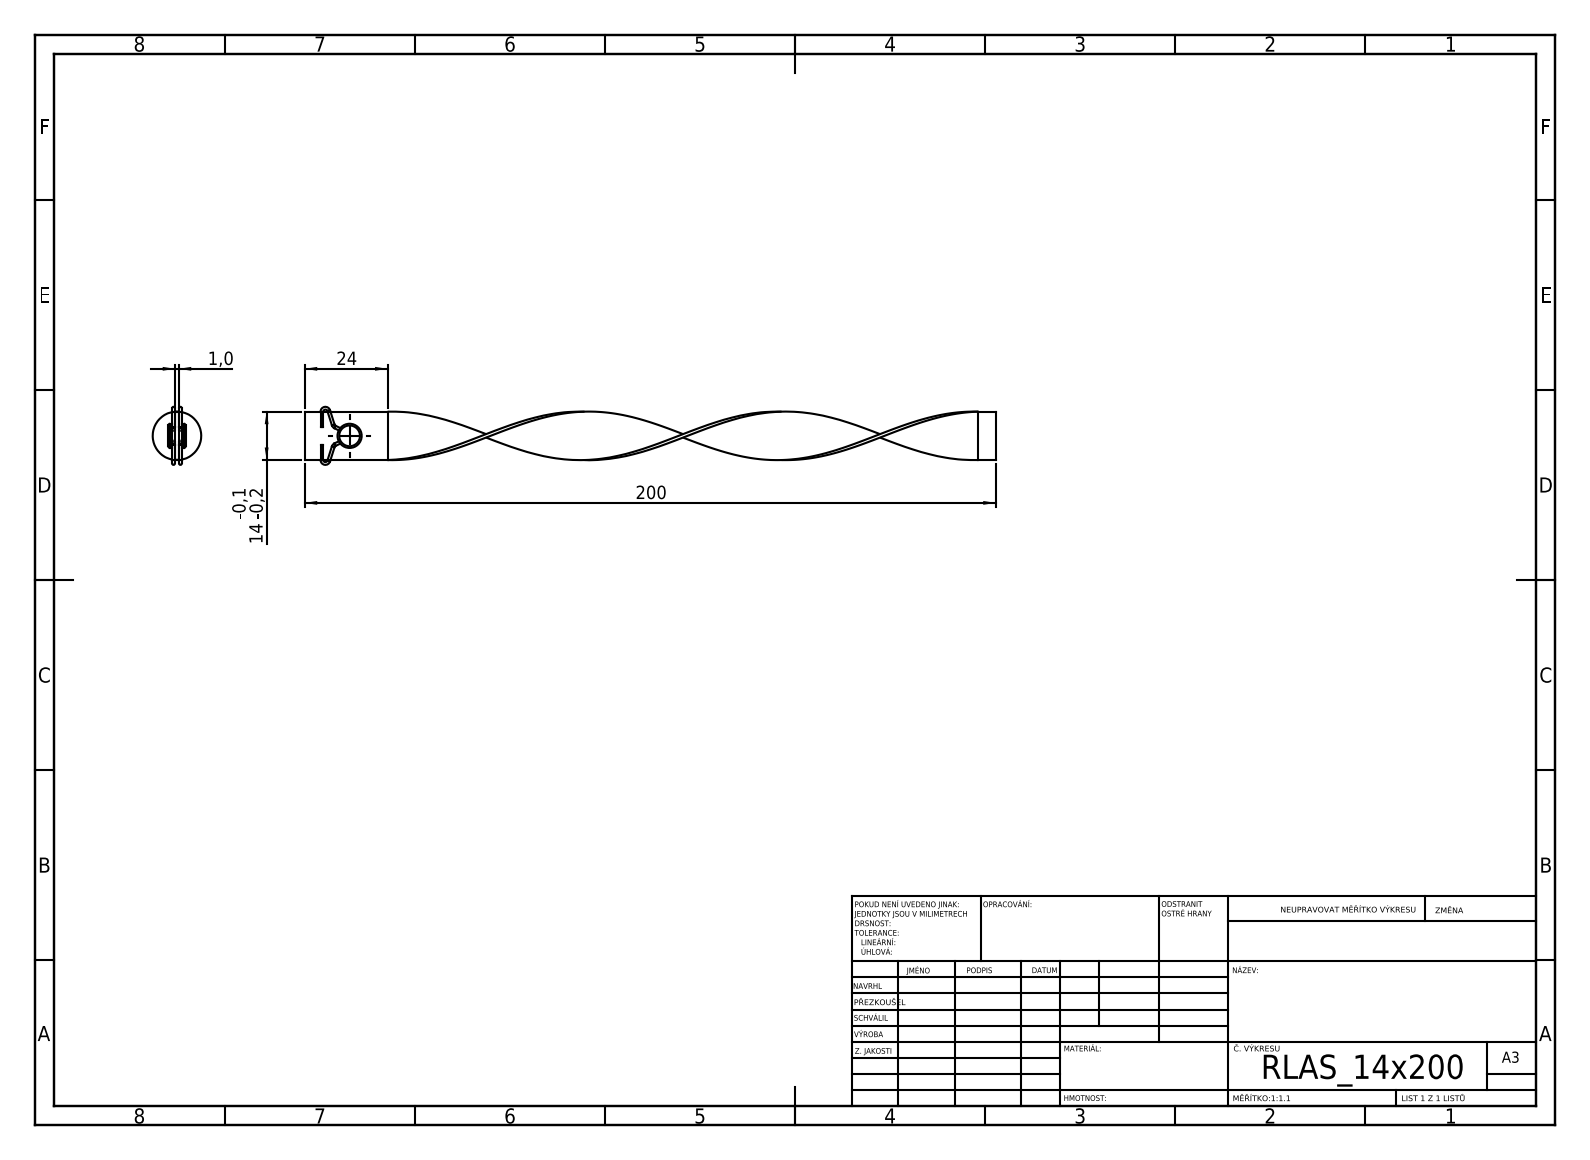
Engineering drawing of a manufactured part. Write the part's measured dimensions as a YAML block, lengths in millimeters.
step_written_by: "SolidWorks 2019 (CONFIG_CONTROL_DESIGN)"
units: millimeters
bodies: {solids: 3, faces: 90, planar: 18, cylindrical: 40, other: 32}
overall_size: [200, 16.8, 14.04]
volume: 2942
surface_area: 6522
round_bosses_or_shafts:
  - {diameter: 0.8, count: 14}
  - {diameter: 7, count: 1}
  - {diameter: 4, count: 1}
face_to_face_distances: [1, 2, 3, 4, 14, 5, 200, 4.45, 9.55, 5.1]
